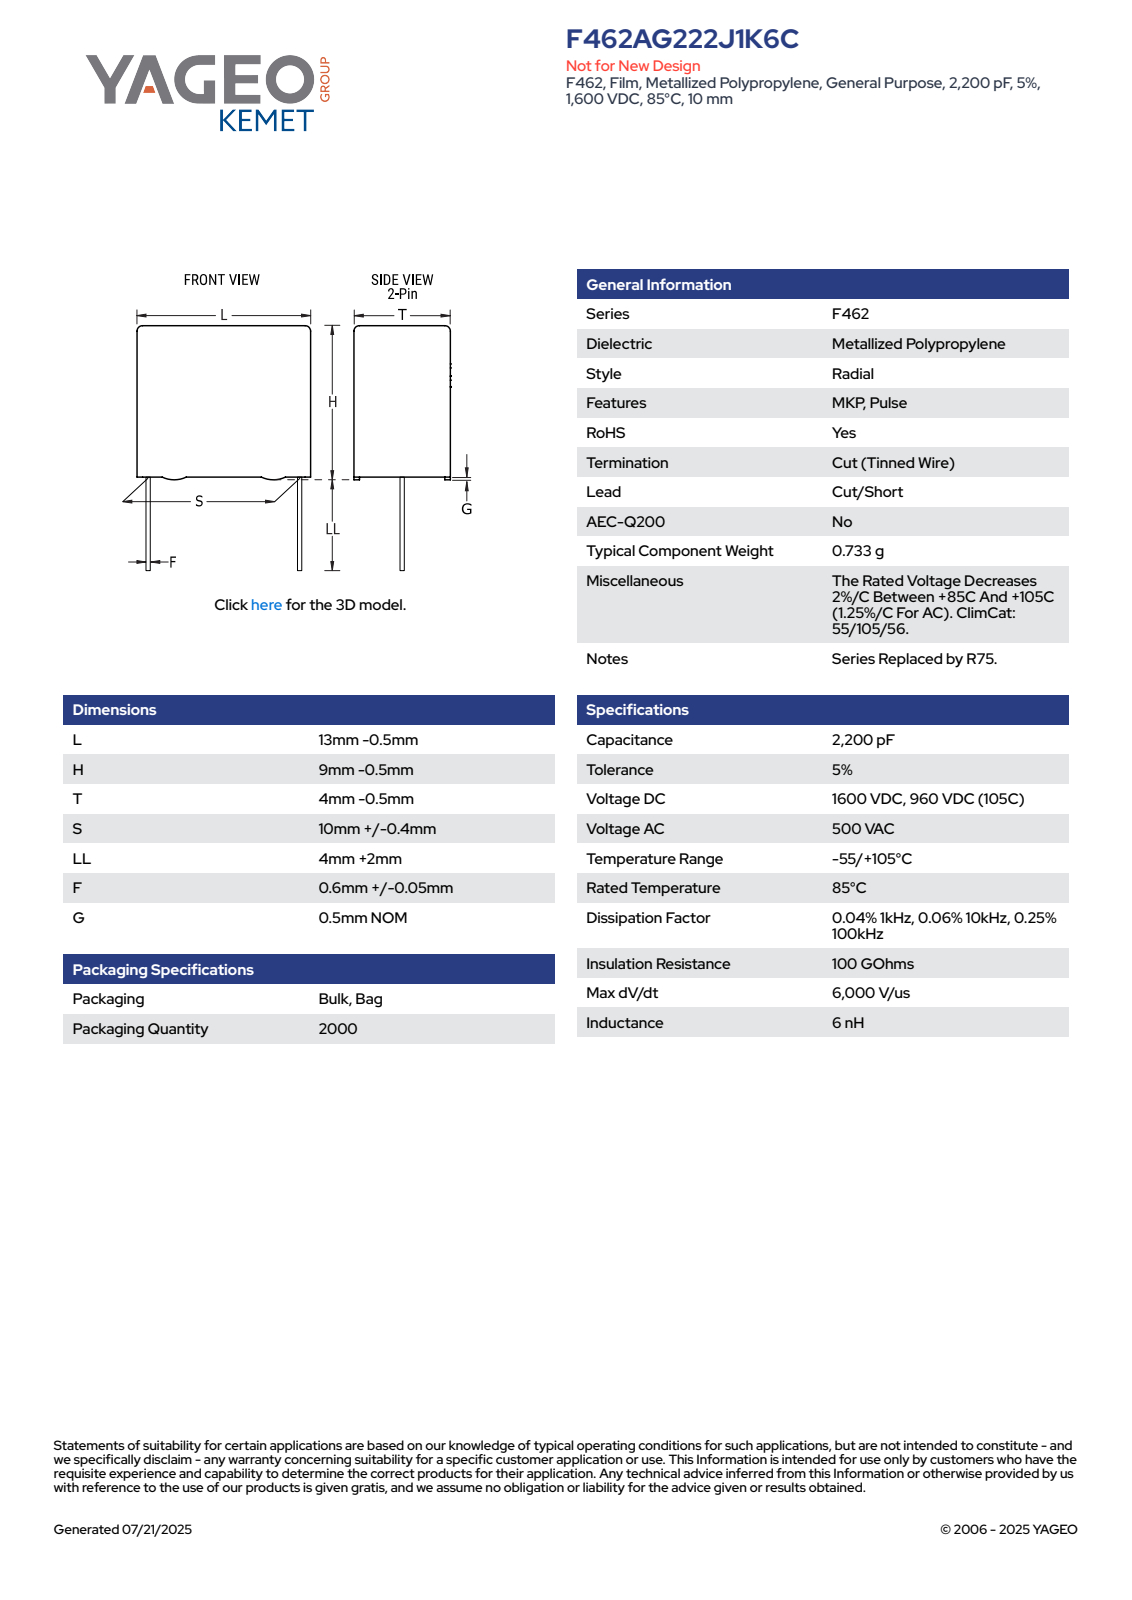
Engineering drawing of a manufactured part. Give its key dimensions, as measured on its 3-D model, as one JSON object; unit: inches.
{"part_name": "CFR_RBG_13X9X4_L12.5H8.5T3.5S10LL6F0.65G0.5", "step_written_by": "SolidWorks 2014 (AUTOMOTIVE_DESIGN)", "units": "inches", "bodies": {"solids": 4, "faces": 89, "planar": 81, "cylindrical": 8, "other": 0}, "overall_size": [0.571, 0.492, 0.138], "volume_in3": 0.022, "surface_area_in2": 0.603, "round_bosses_or_shafts": [[0.026, 2]], "partial_cylinders_radius": [[0.02, 4]], "face_to_face_distances": [0.138, 0.315, 0.492, 0.13, 0.122, 0.02, 0.335, 0.236, 0.256, 0.571]}
